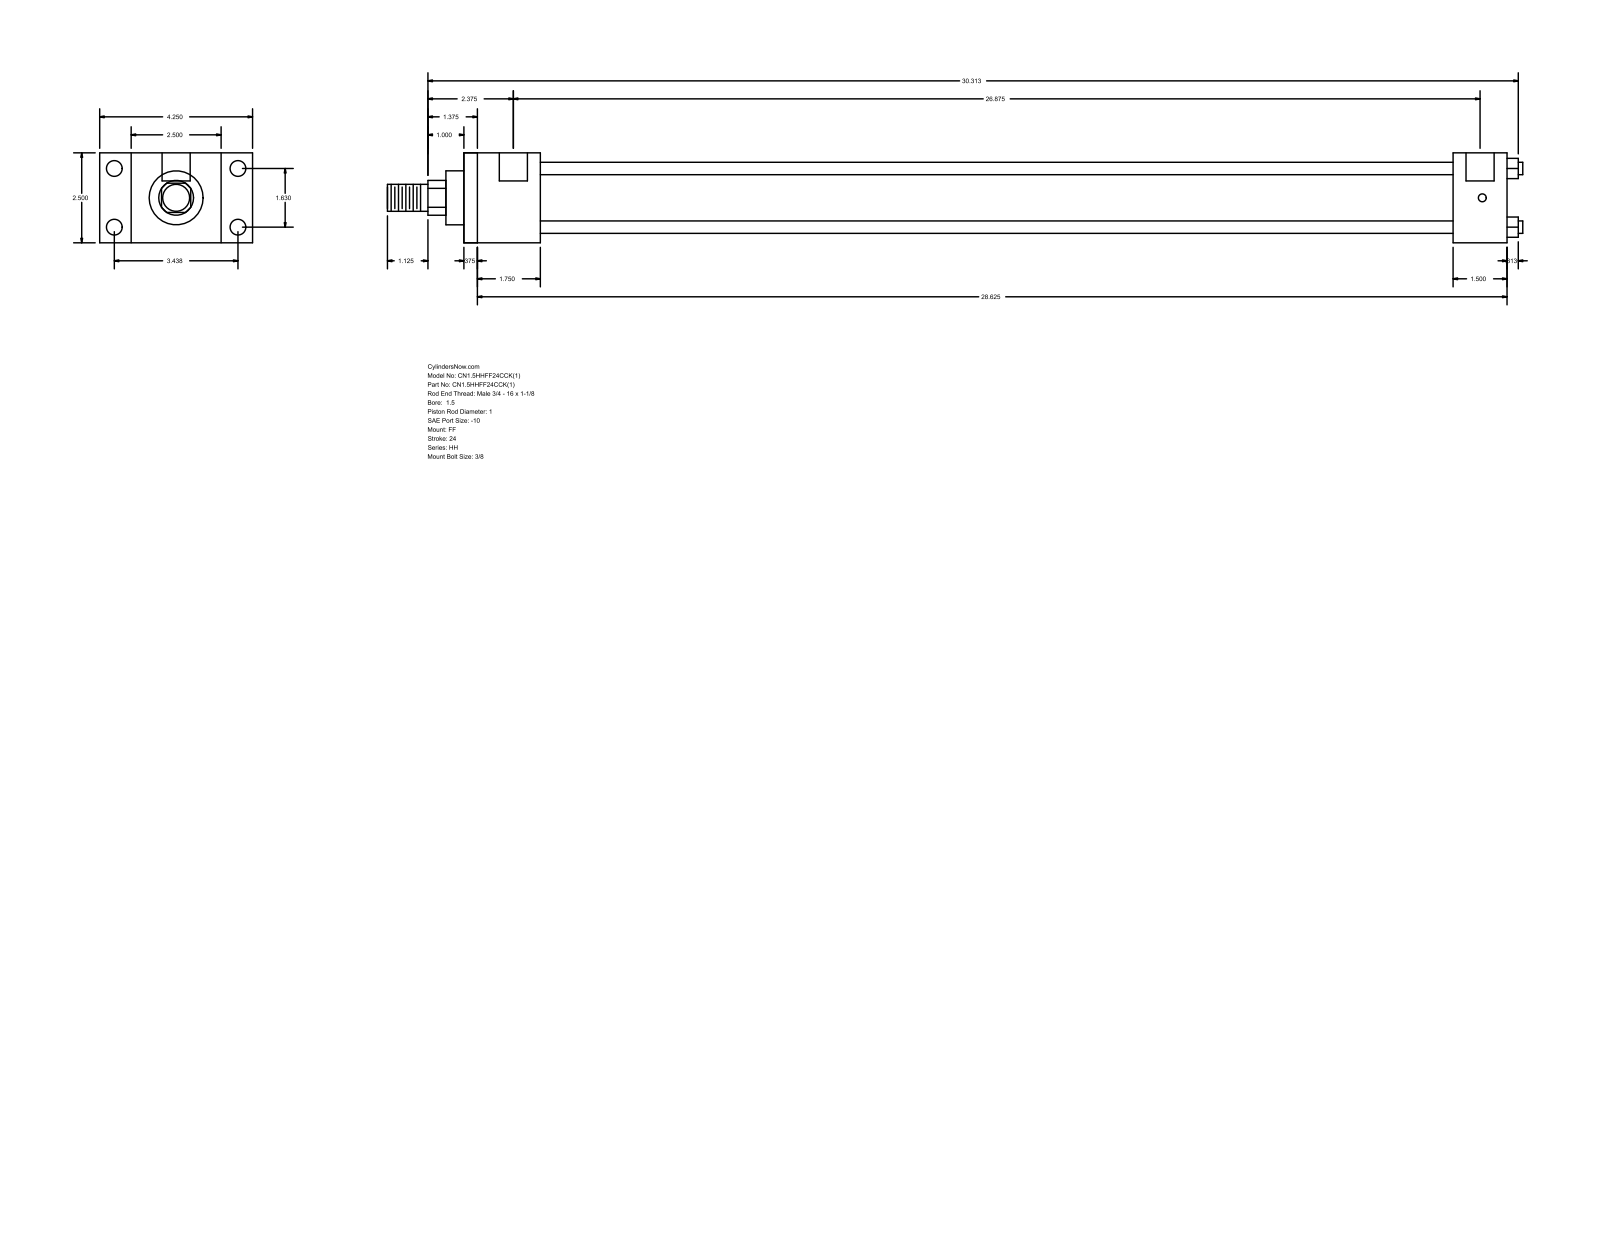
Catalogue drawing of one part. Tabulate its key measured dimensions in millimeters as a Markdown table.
| quantity | value |
| --- | --- |
| part name | HH_FF__0150_1 |
| STEP written by | GSSL Pune (CONFIG_CONTROL_DESIGN) |
| units | millimeters |
| bodies | 0 solids, 92 faces (64 planar, 28 cylindrical, 0 other) |
| overall size | 801.69 × 107.95 × 63.5 |
| round holes (diameter × count) | 5.56 × 4, 11.13 × 4, 19.84 × 2 |
| round bosses / shafts (diameter × count) | 8.76 × 4, 44.45 × 1, 38.1 × 1, 25.4 × 1, 19.05 × 1 |
| partial cylindrical surfaces (radius × count) | 12.29 × 1 |
| main face-to-face distances | 63.5, 736.6, 9.52, 727.08, 38.1, 53.98, 44.46, 682.62, 698.5, 688.98 |
| hole center spacings | 1.59, 41.4, 87.32, 96.64, 684.21, 685.8, 682.62 |
